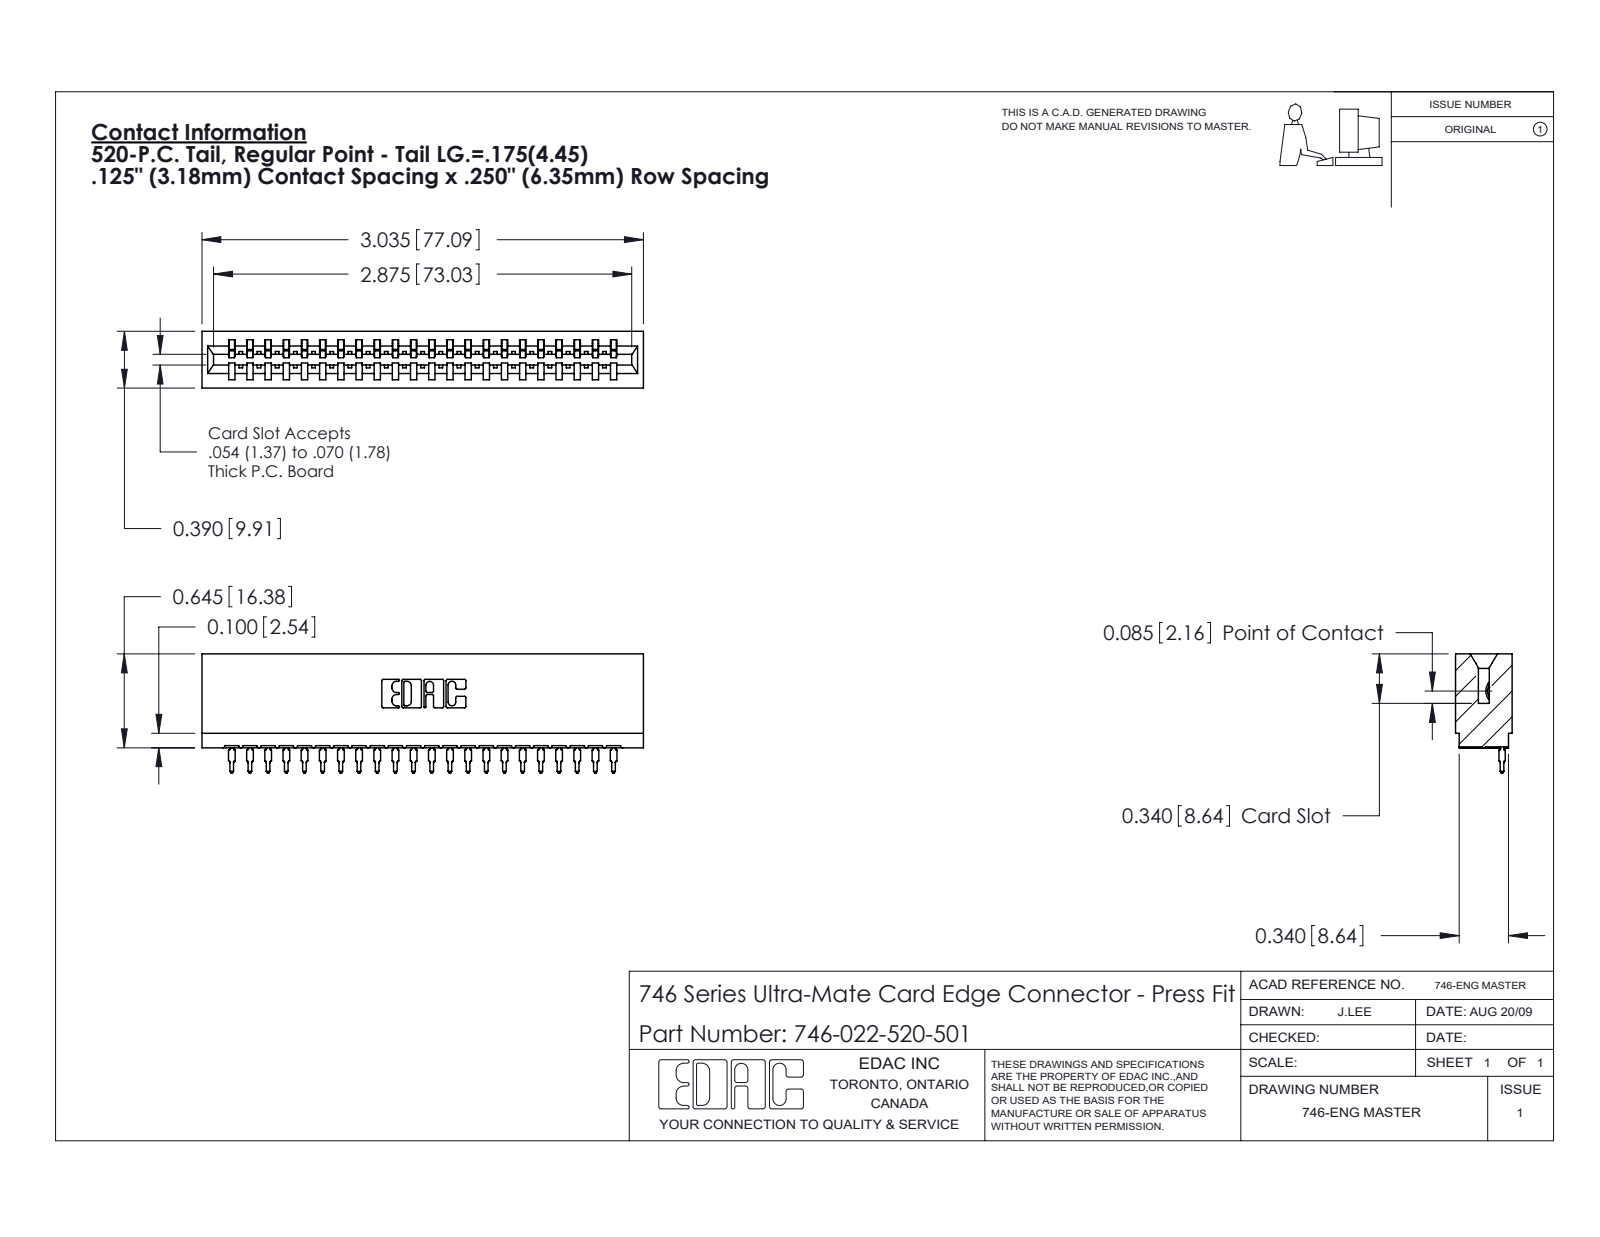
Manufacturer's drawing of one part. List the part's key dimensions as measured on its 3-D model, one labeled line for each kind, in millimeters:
Part name (STEP PRODUCT): 746 Part_.340 Slot Depth - 01; 746-022-520-501; 746-292-001_520
STEP written by: SolidWorks 2020 (CONFIG_CONTROL_DESIGN)
Units: millimetres
Bodies: 23 solids, 2473 faces (1441 planar, 460 cylindrical, 572 other)
Overall size (bounding box): 77.1 × 20.8 × 9.9
Volume: 8 750 mm³ · Surface area: 11 320 mm²
Partial cylindrical surfaces — rounded edges, fillets, slot ends (radius × count): R0.5 ×44, R0.4 ×23, R0.3 ×22, R0.2 ×6, R0.8 ×6, R0.1 ×4, R0.3 ×4, R0.7 ×3
Main face-to-face distances: 1.4, 6.4, 9.9, 8.5, 0.6, 7.8, 3.2, 9.5, 3.2, 12.7
